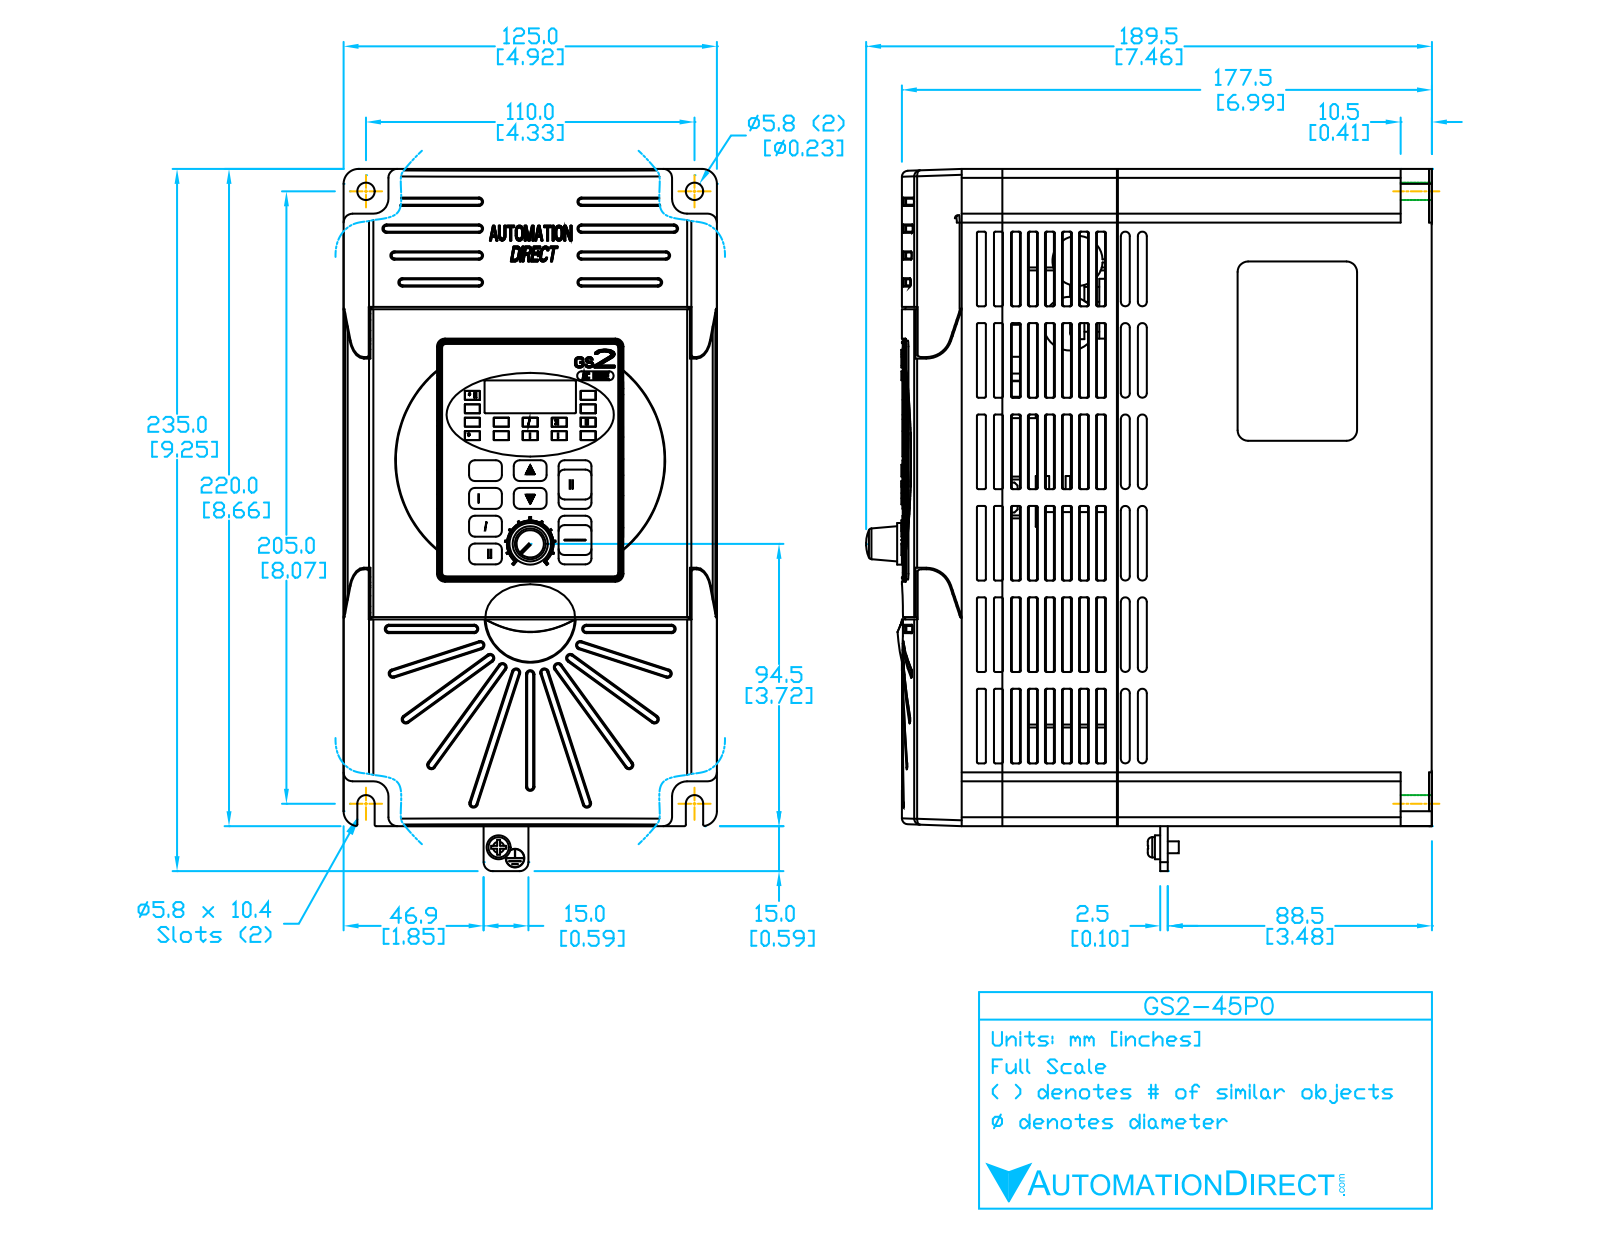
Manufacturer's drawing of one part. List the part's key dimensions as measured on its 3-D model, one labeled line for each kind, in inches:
Part name (STEP PRODUCT): GS2-45P0
STEP written by: SolidWorks 2013 (AUTOMOTIVE_DESIGN)
Units: inches
Bodies: 1 solid, 792 faces (356 planar, 218 cylindrical, 218 other)
Overall size (bounding box): 9.25 × 7.485 × 4.92
Volume: 282.9 in³ · Surface area: 350.8 in²
Round holes (diameter × count): ⌀0.23 ×2, ⌀3.2 ×1
Round bosses / shafts (diameter × count): ⌀0.545 ×1, ⌀0.258 ×1, ⌀0.15 ×1
Partial cylindrical surfaces — rounded edges, fillets, slot ends (radius × count): R0.06 ×40, R0.04 ×38, R0.125 ×12, R0.2 ×8, R0.019 ×6, R0.064 ×6, R0.25 ×6, R0.1 ×4
Main face-to-face distances: 0.015, 4.905, 4.92, 6.181, 8.645, 4.89, 8.66, 6.17, 0.58, 0.565
Hole centre spacings: 4.33
